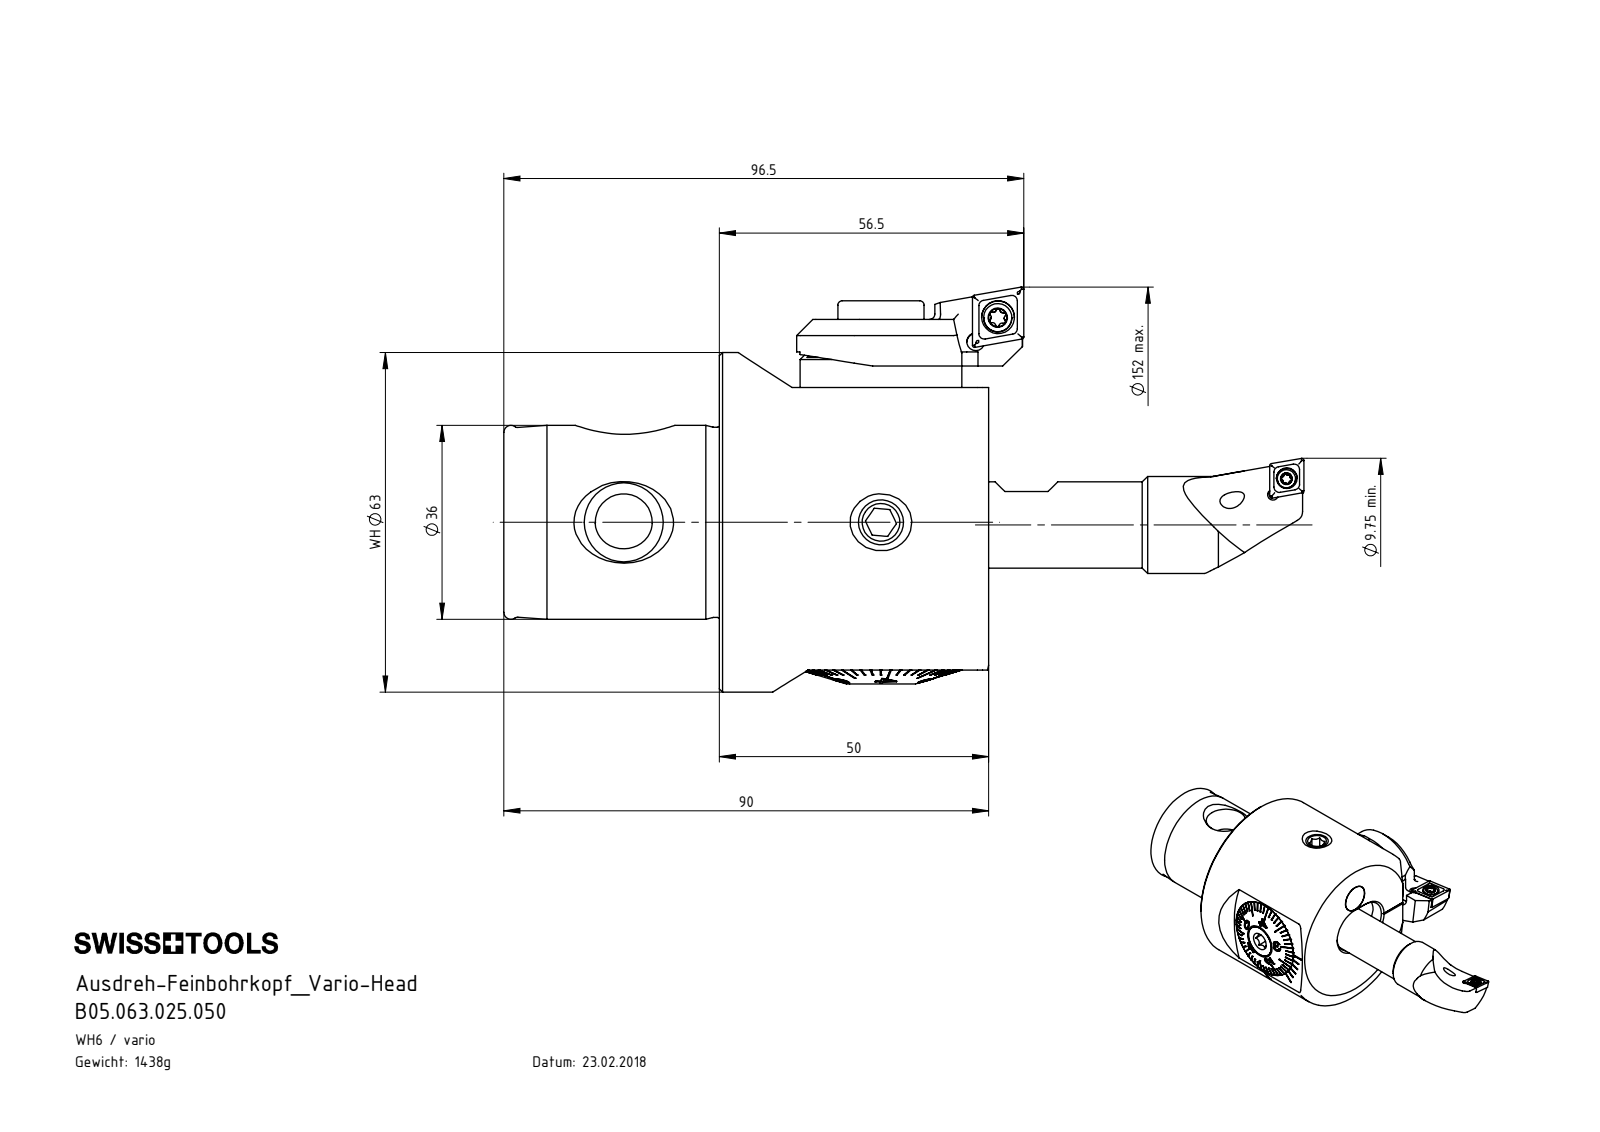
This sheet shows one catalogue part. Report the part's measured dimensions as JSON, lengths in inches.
{"part_name": "A55-BG2.011.016_D; AV6-BG2.014.011_A_Abgedreht; ISO 4026 - M5 x 16; AV6-BG1.001.052_C (+8 more)", "step_written_by": "SolidWorks 2017 (CONFIG_CONTROL_DESIGN)", "units": "inches", "bodies": {"solids": 20, "faces": 1016, "planar": 417, "cylindrical": 202, "other": 397}, "overall_size": [5.846, 2.959, 2.48], "volume_in3": 11.36, "surface_area_in2": 89.57, "round_holes": [[0.13, 3], [0.118, 2], [0.335, 2], [0.079, 1], [0.081, 1], [0.098, 1], [0.11, 1], [0.152, 1], [0.157, 1], [0.165, 1], [0.173, 1], [0.236, 1]], "round_bosses_or_shafts": [[0.709, 2], [0.394, 2], [2.48, 1], [1.417, 1], [1.39, 1], [1.18, 1], [1.177, 1], [0.984, 1]], "partial_cylinders_radius": [[0.008, 6], [0.013, 6], [0.023, 6], [0.039, 6], [0.014, 5], [0.126, 5], [0.02, 4], [0.335, 2]], "face_to_face_distances": [1.969, 0.22, 2.028, 1.807, 0.256, 0.157, 0.098, 2.236, 2.016, 0.209], "hole_center_spacings": [0.153, 0.157, 0.239, 0.243, 0.413, 0.571]}
